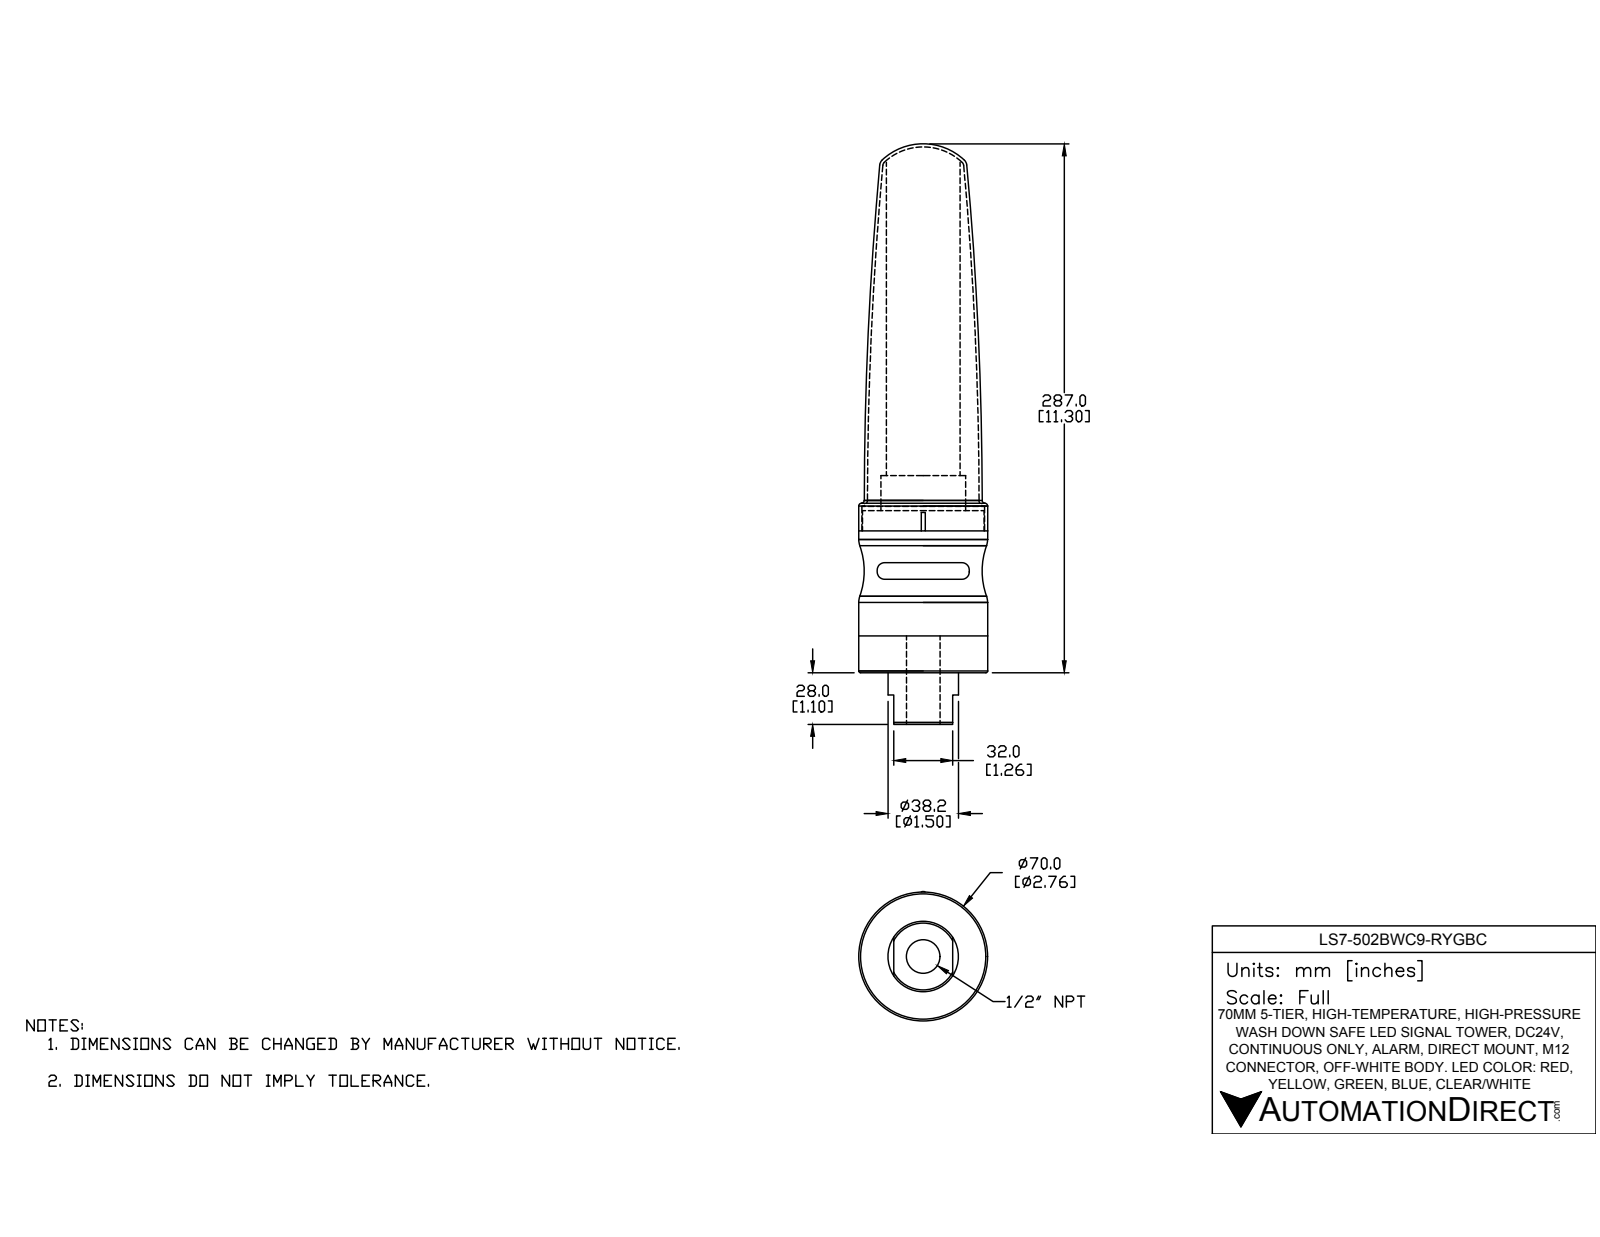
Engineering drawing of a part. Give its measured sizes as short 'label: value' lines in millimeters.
name: LS7-502BWC9-RYGBC
written by: SolidWorks 2016 (AUTOMOTIVE_DESIGN)
unit: mm
bodies: 4 solids, 77 faces (22 planar, 26 cylindrical, 29 other)
size: 315 × 70.3 × 70
volume: 636 849 mm³; area: 146 517 mm²
holes: 1× ⌀18.2, 1× ⌀66.6
bosses: 1× ⌀70, 1× ⌀66, 1× ⌀46, 1× ⌀40, 1× ⌀38.2
rounds: 4× R4, 1× R1, 1× R2
face distances: 87, 20, 107, 88, 68, 19, 9, 277, 257, 189
